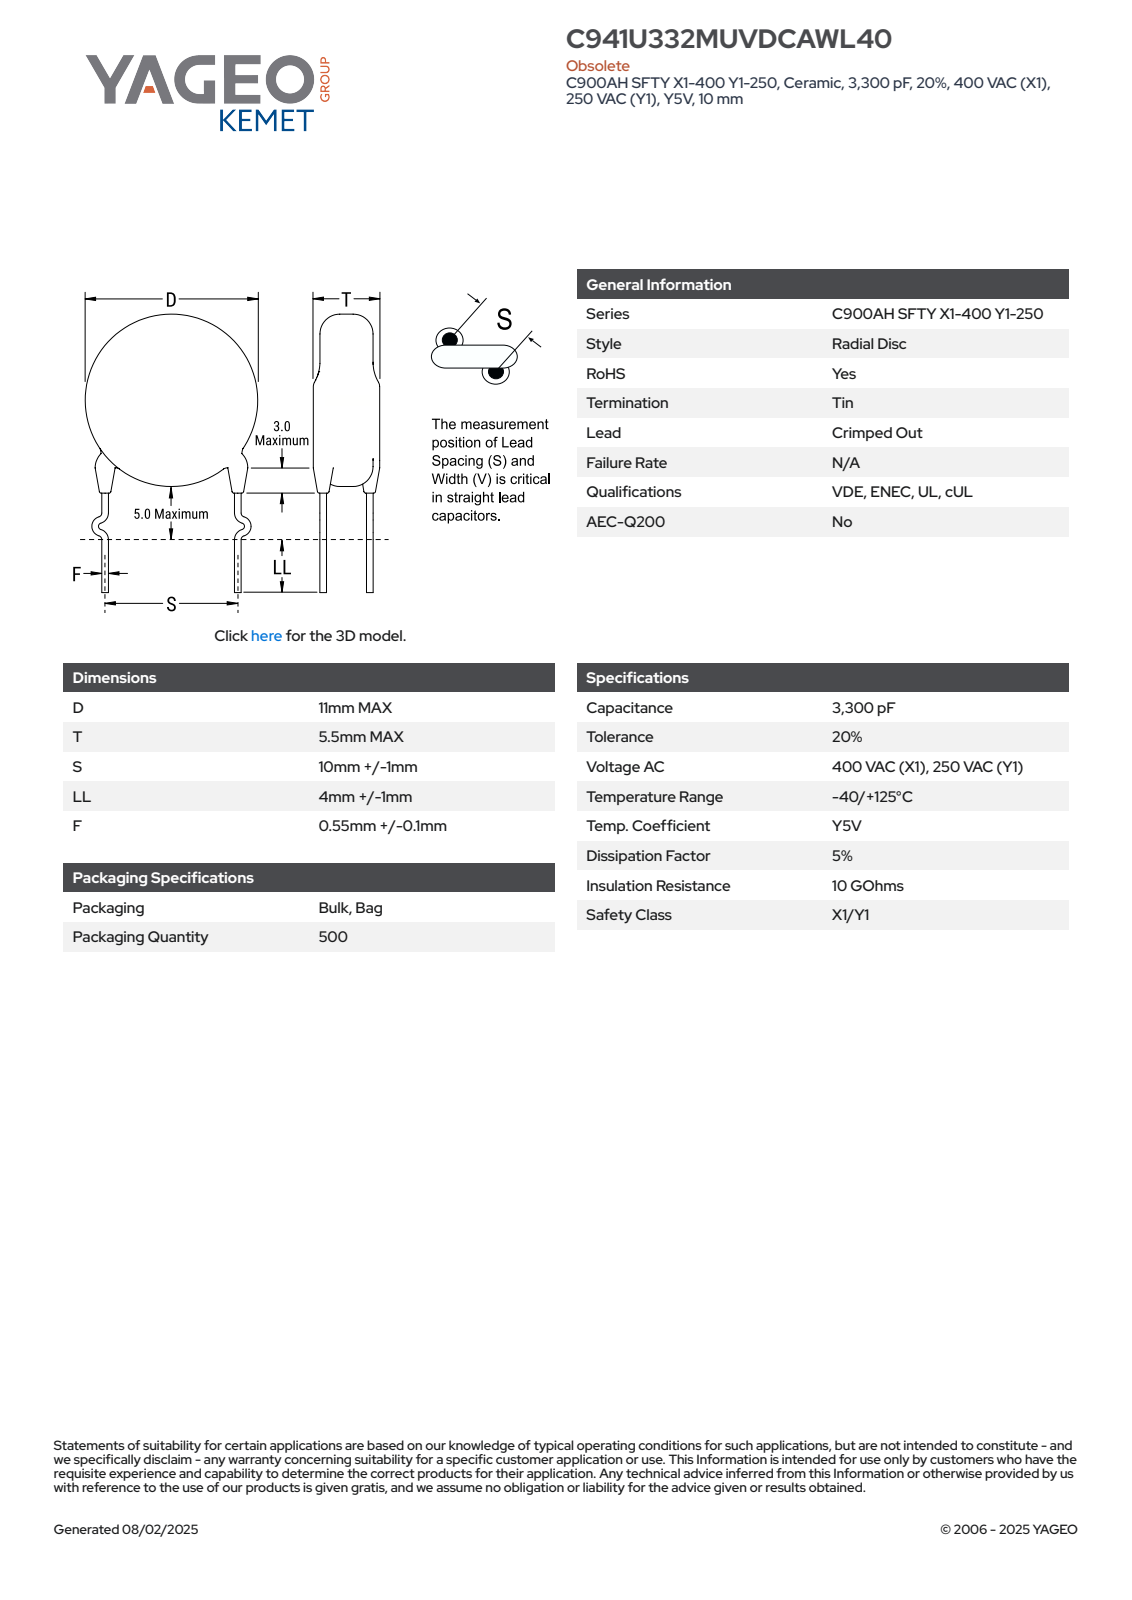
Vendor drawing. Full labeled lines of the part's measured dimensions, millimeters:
Part name (STEP PRODUCT): CCD_KCOC900_D11T5.5S10LL5F0.55
STEP written by: SolidWorks 2014 (AUTOMOTIVE_DESIGN)
Units: millimetres
Bodies: 4 solids, 87 faces (63 planar, 6 cylindrical, 18 other)
Overall size (bounding box): 21 × 14.69 × 5.5
Volume: 523 mm³ · Surface area: 428 mm²
Round bosses / shafts (diameter × count): ⌀1.2 ×2, ⌀11 ×1
Main face-to-face distances: 5.5, 1.14, 6.08, 4.94, 0.32, 0.92, 4.67, 2.36, 3.39, 3.53
